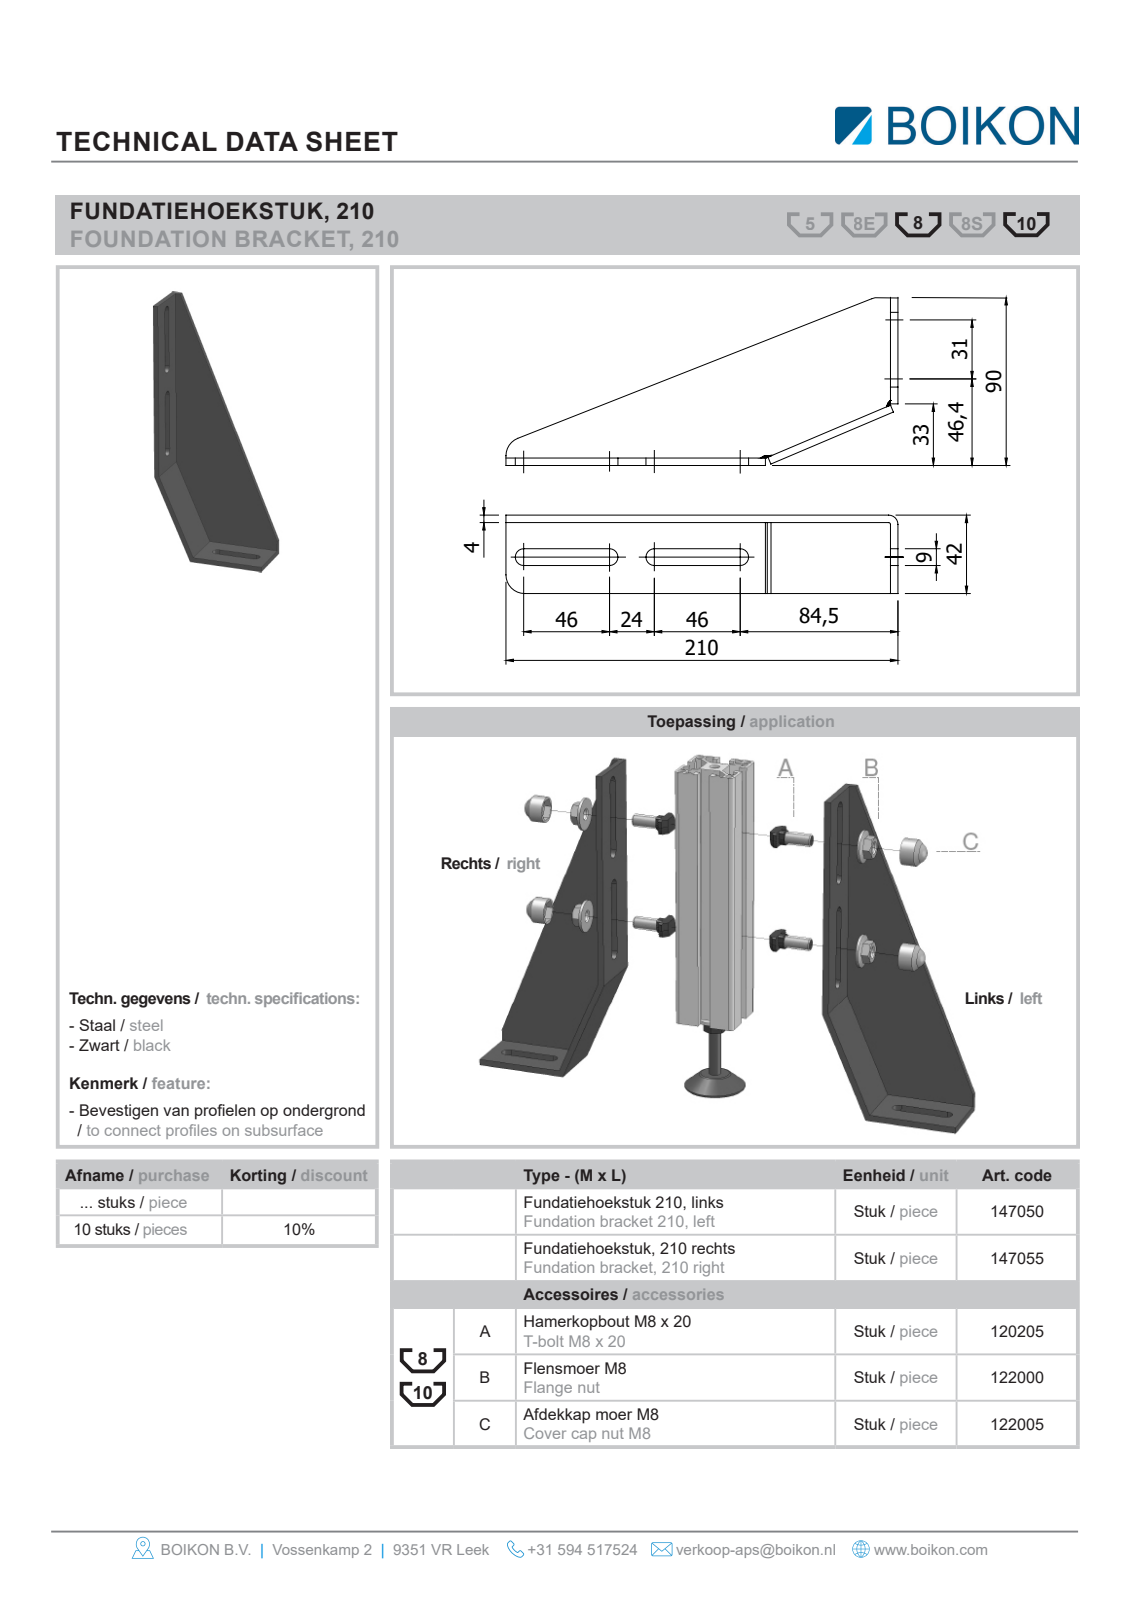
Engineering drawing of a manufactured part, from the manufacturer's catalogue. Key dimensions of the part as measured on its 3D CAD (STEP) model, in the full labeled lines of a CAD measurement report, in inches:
Part name (STEP PRODUCT): Root; 147055Fundatie hoekstuk, 210 RechtsBOIKON
STEP written by: HiCAD 2013 1802.4 Build 509 (AUTOMOTIVE_DESIGN)
Units: inches
Bodies: 1 solid, 24 faces (18 planar, 6 cylindrical, 0 other)
Overall size (bounding box): 8.268 × 4.429 × 1.614
Volume: 4.531 in³ · Surface area: 63.21 in²
Partial cylindrical surfaces — rounded edges, fillets, slot ends (radius × count): R0.177 ×6
Main face-to-face distances: 0.157, 0.158, 1.614, 1.457, 0.551, 0.906, 0.709, 1.063, 0.354, 3.386
